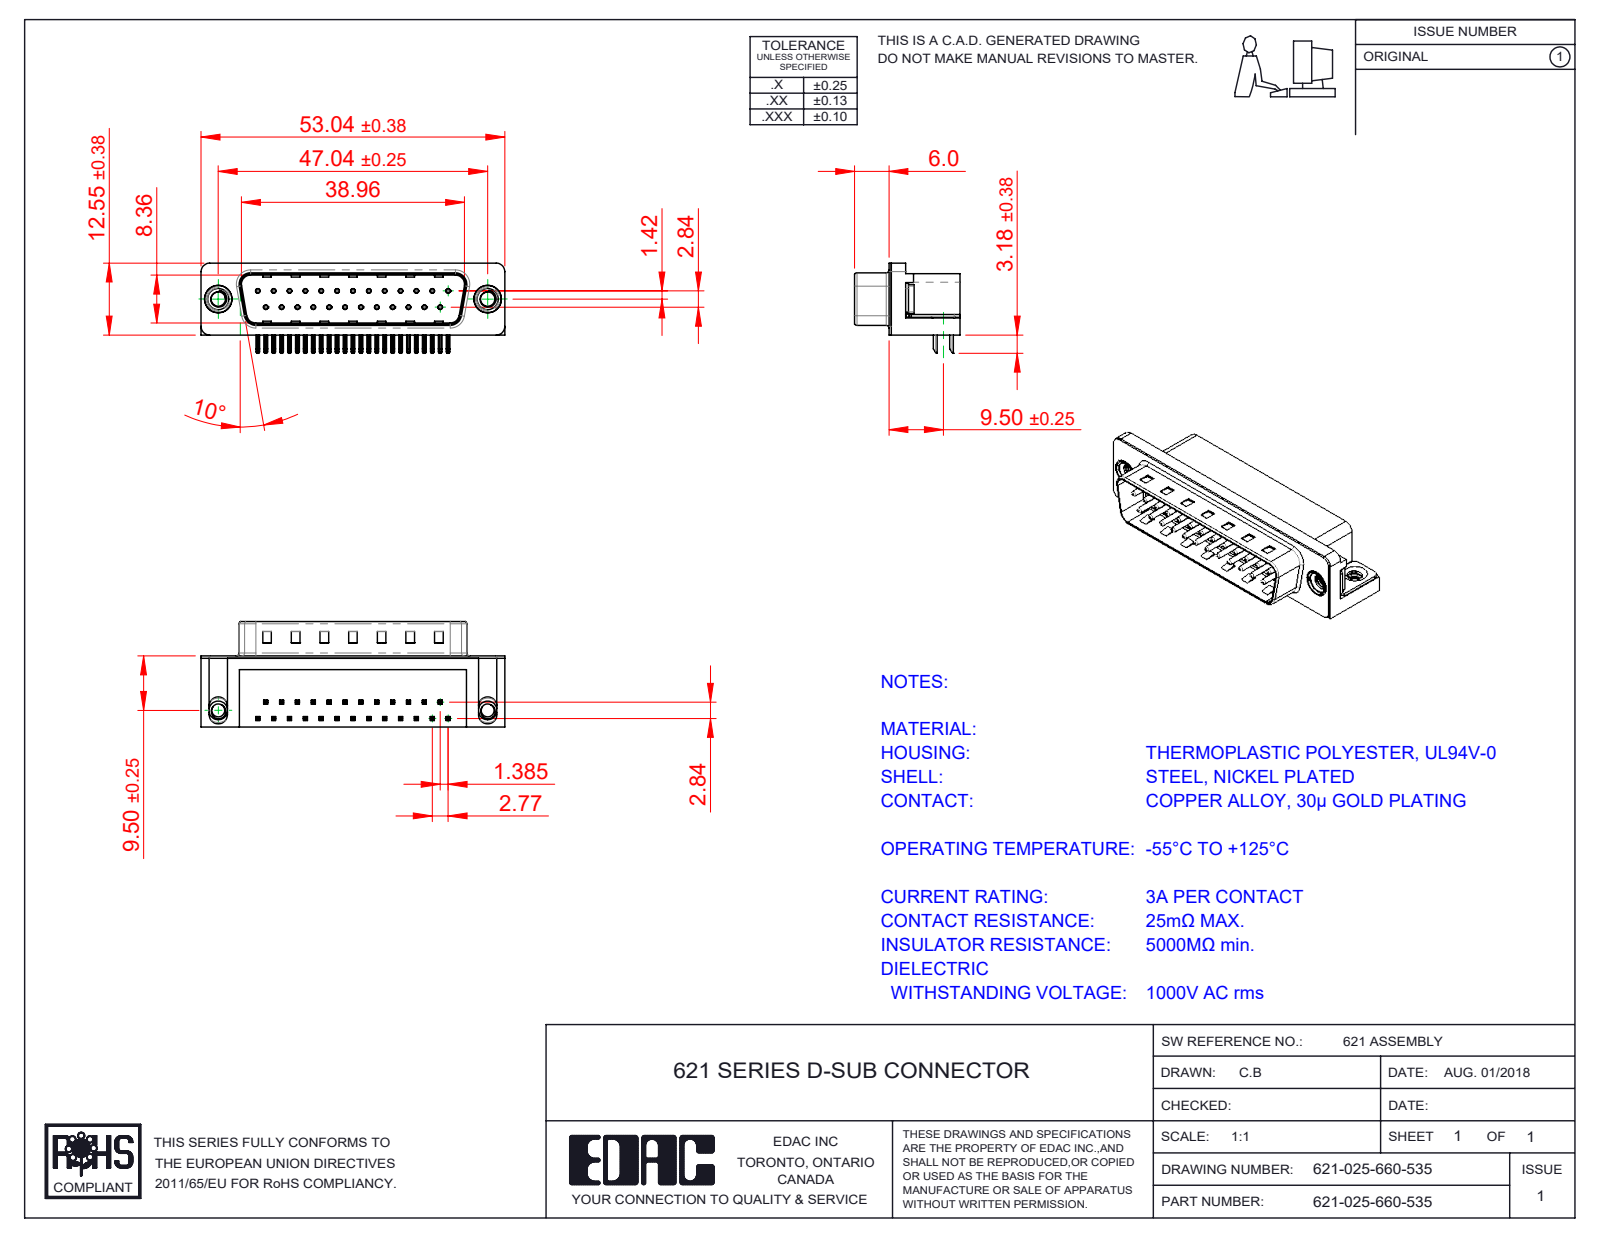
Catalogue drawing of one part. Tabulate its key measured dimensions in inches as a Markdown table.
| quantity | value |
| --- | --- |
| part name | 621 Contact Bottom; 621-025-660-535; 621 2 Prong Board Lock; 621 M3 Threaded Rivet (+3 more) |
| STEP written by | SolidWorks 2016 (CONFIG_CONTROL_DESIGN) |
| units | inches |
| bodies | 31 solids, 2303 faces (1437 planar, 671 cylindrical, 195 other) |
| overall size | 2.088 × 0.724 × 0.64 |
| volume | 0.387 in³ |
| surface area | 11.92 in² |
| round holes (diameter × count) | 0.014 × 25, 0.031 × 25, 0.098 × 2, 0.157 × 2, 0.189 × 2, 0.197 × 2 |
| round bosses / shafts (diameter × count) | 0.03 × 25, 0.193 × 2, 0.187 × 2, 0.154 × 2 |
| partial cylindrical surfaces (radius × count) | 0.01 × 108, 0.005 × 50, 0.039 × 16, 0.02 × 14, 0.063 × 8, 0.059 × 7, 0.013 × 4, 0.035 × 4 |
| main face-to-face distances | 0.016, 0.472, 0.407, 0.083, 0.345, 0.412, 0.428, 0.067, 0.488, 0.354 |
| hole center spacings | 0.124, 0.109, 0.218, 0.327, 0.436, 0.545, 0.654, 0.198 |
